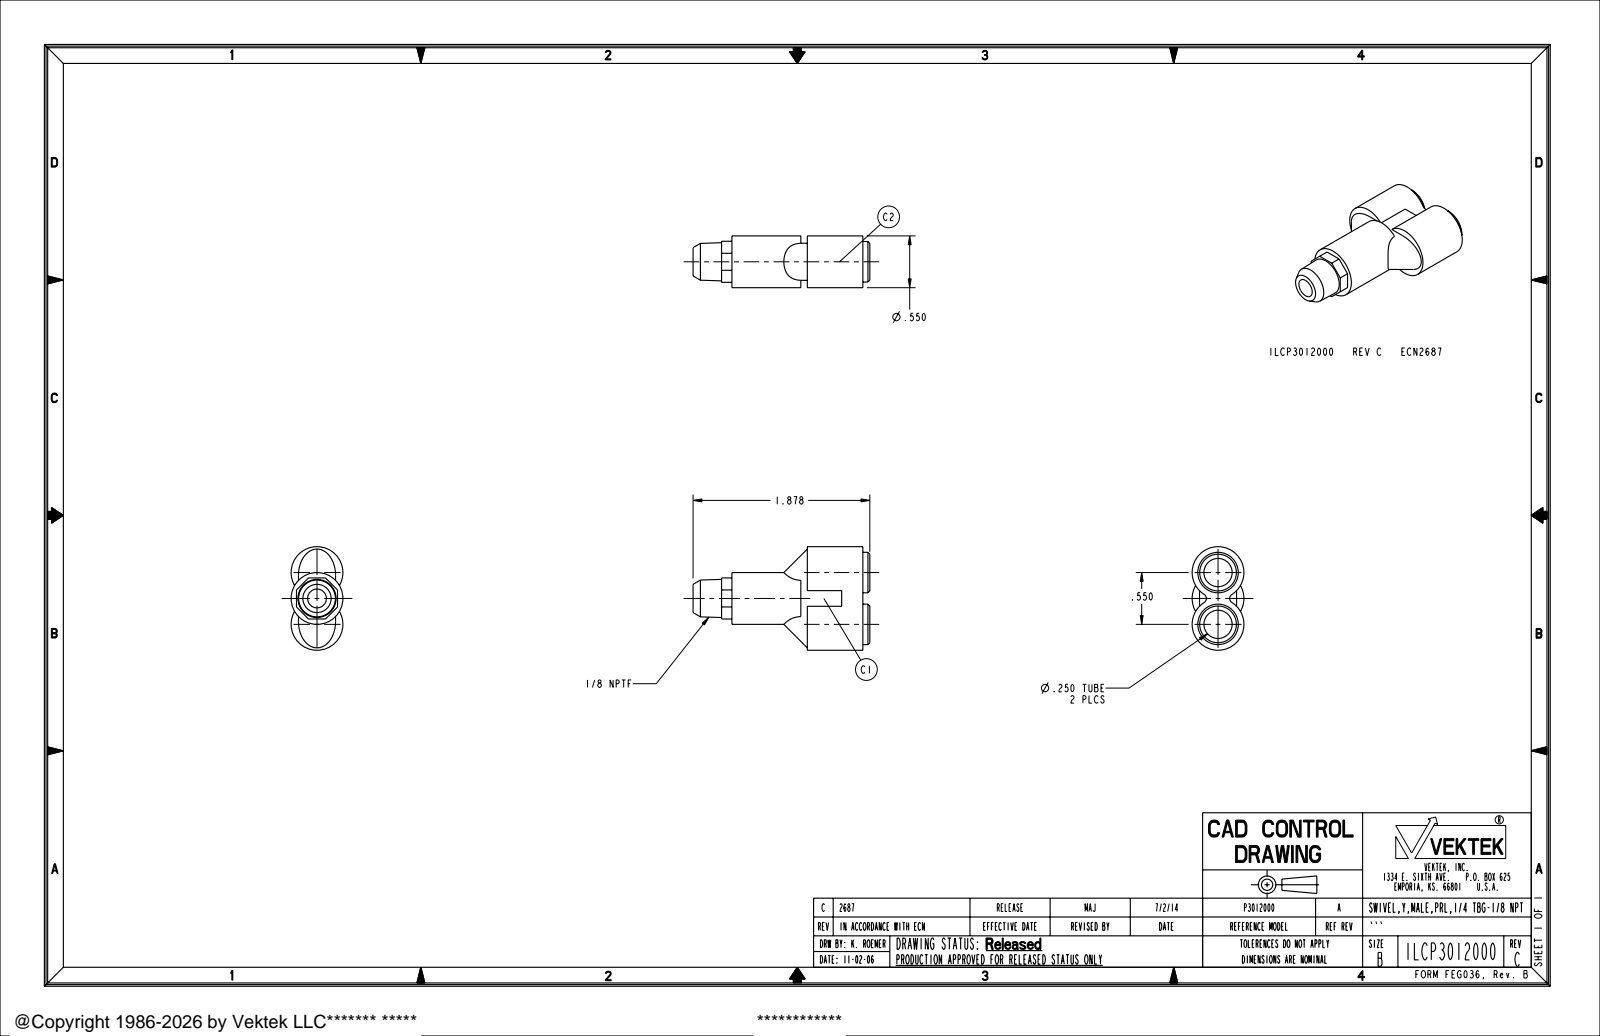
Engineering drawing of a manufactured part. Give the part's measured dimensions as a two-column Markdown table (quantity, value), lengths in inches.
| quantity | value |
| --- | --- |
| part name | ILCP3012000 |
| STEP written by | PRO/ENGINEER BY PARAMETRIC TECHNOLOGY CORPORATION, 2013320 (CONFIG_CONTROL_DESIGN) |
| units | inches |
| bodies | 1 solid, 51 faces (25 planar, 18 cylindrical, 8 other) |
| overall size | 1.878 × 1.1 × 0.55 |
| volume | 0.453 in³ |
| surface area | 6.584 in² |
| round holes (diameter × count) | 0.3 × 2, 0.2 × 1 |
| round bosses / shafts (diameter × count) | 0.55 × 3, 0.43 × 2 |
| partial cylindrical surfaces (radius × count) | 0.05 × 2, 0.197 × 2 |
| main face-to-face distances | 0.526, 0.59, 0.064, 0.074, 0.6, 0.664, 0.394, 1.465, 1.391, 0.865 |
| hole center spacings | 0.275, 0.55 |
